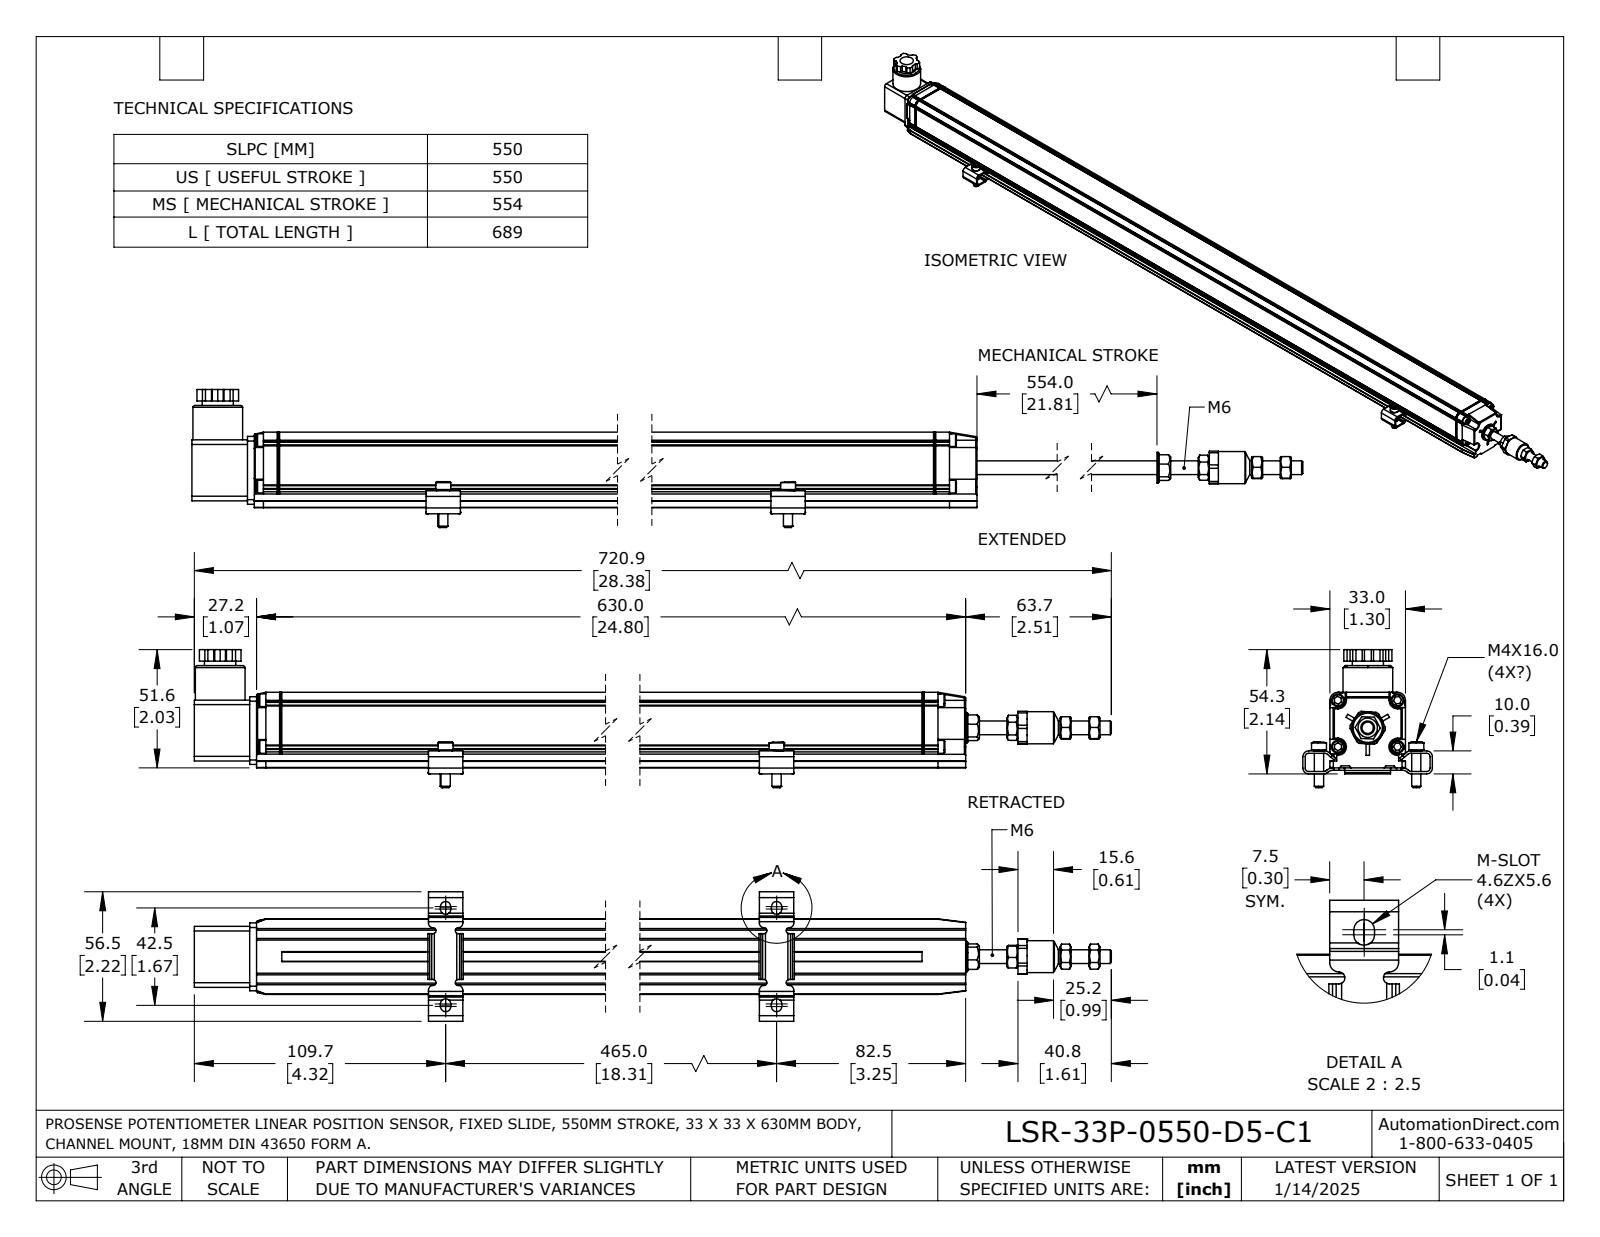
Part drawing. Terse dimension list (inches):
name: LSR-33P-0550-D5-C1
written by: SolidWorks 2023 (AUTOMOTIVE_DESIGN)
unit: in
bodies: 14 solids, 995 faces (641 planar, 269 cylindrical, 85 other)
size: 28.38 × 2.37 × 2.224
volume: 38.84 in³; area: 241.2 in²
holes: 4× ⌀0.106, 4× ⌀0.13, 1× ⌀0.169, 1× ⌀0.205, 1× ⌀0.209, 1× ⌀0.232, 1× ⌀0.276, 1× ⌀0.285, 1× ⌀0.394, 1× ⌀0.413, 1× ⌀0.573, 1× ⌀0.602
bosses: 5× ⌀0.157, 5× ⌀0.118, 4× ⌀0.256, 4× ⌀0.22, 1× ⌀0.854, 1× ⌀0.551, 1× ⌀0.535, 1× ⌀0.528
rounds: 28× R0.079, 23× R0.02, 16× R0.008, 8× R0.051, 8× R0.059, 8× R0.089, 8× R0.118, 4× R0.039
face distances: 1.299, 0.118, 0.22, 1.181, 1.079, 0.039, 0.079, 0.142, 1.22, 0.185
hole spacings: 0.047, 0.583, 0.607, 0.696, 0.73, 0.799, 1.024, 1.299
